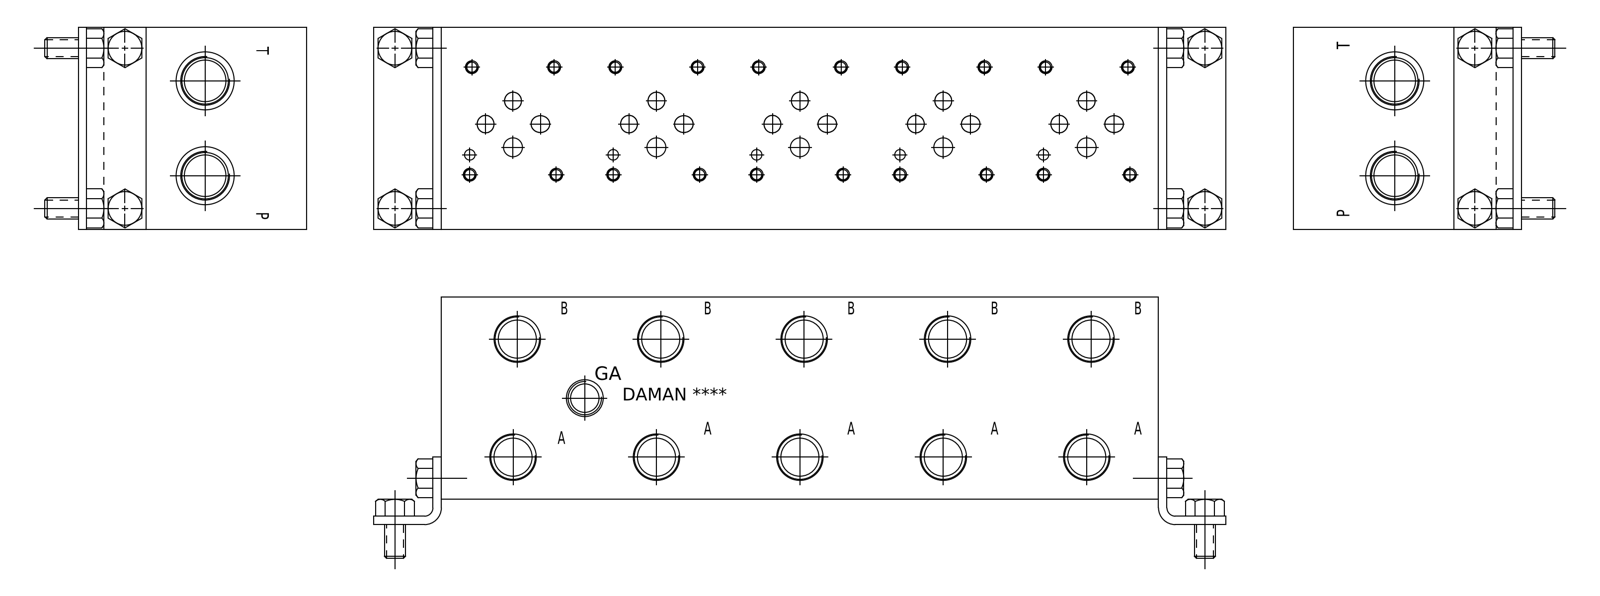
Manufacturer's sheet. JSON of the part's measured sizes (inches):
{"part_name": "Part_AD03S052P_3D", "step_written_by": "Autodesk Inventor 2019 (AUTOMOTIVE_DESIGN)", "units": "inches", "bodies": {"solids": 1, "faces": 821, "planar": 439, "cylindrical": 107, "other": 275}, "overall_size": [10.625, 3, 3], "volume_in3": 90.56, "surface_area_in2": 183.9, "round_holes": [[0.149, 20], [0.19, 20], [0.25, 15], [0.563, 10], [0.681, 10], [0.156, 5], [0.281, 5], [0.257, 2], [0.312, 2], [0.625, 2], [0.688, 2], [0.85, 2]], "face_to_face_distances": [3, 10.625, 0.462, 2.538, 0.605, 10.02, 0.039, 0.422, 2.961, 9.415], "hole_center_spacings": [4.25, 2.125, 2.125, 6.375, 6.375, 8.5, 2.233, 3.858]}
